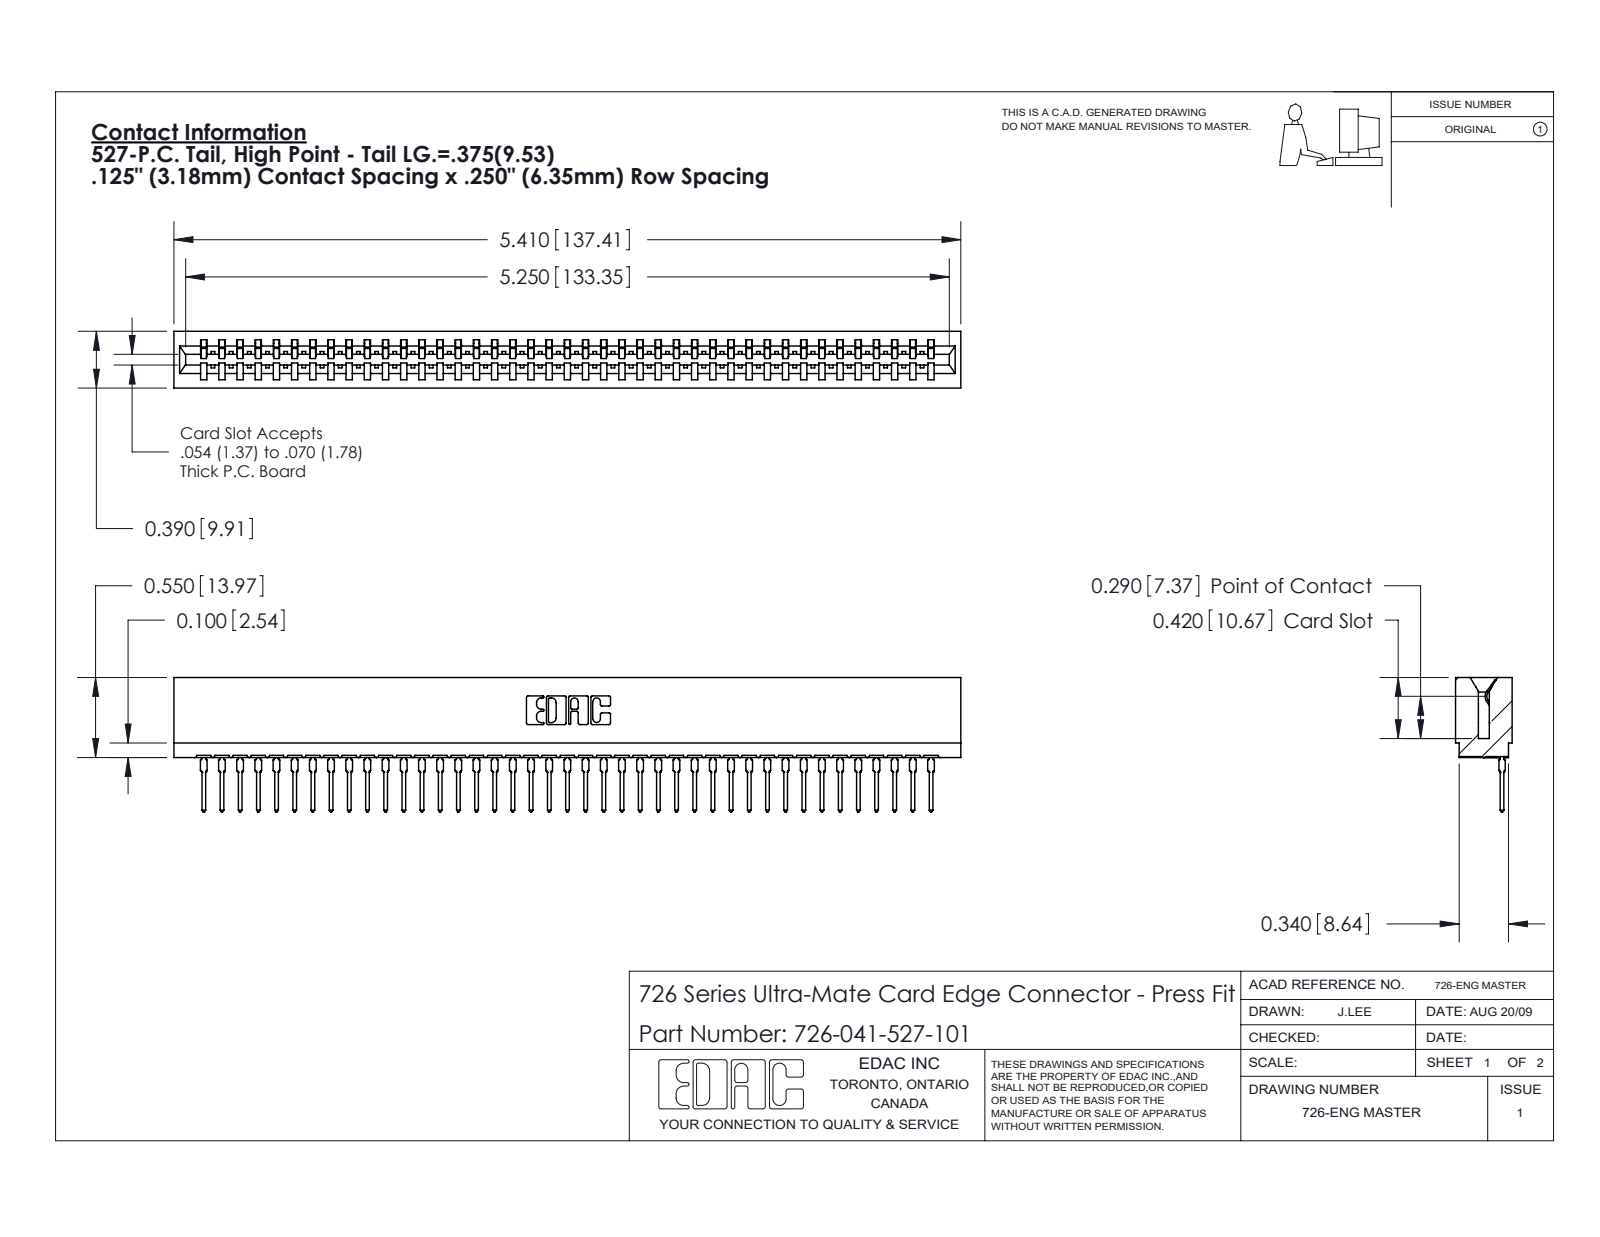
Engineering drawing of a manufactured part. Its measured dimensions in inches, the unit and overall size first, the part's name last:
Units: inches
Overall size (bounding box): 5.41 × 0.924 × 0.39
Partial cylindrical surfaces — rounded edges, fillets, slot ends (radius × count): R0.021 ×82, R0.015 ×42, R0.01 ×22, R0.007 ×6, R0.031 ×6, R0.005 ×4, R0.011 ×4, R0.026 ×3
Main face-to-face distances: 0.057, 0.333, 0.39, 0.025, 0.307, 0.25, 0.275, 0.083, 0.365, 0.032
Volume: 0.751 in³ · Surface area: 29.47 in²
Bodies: 42 solids, 4525 faces (2638 planar, 821 cylindrical, 1066 other)
Part name (STEP PRODUCT): 746-292-001_527; 726 Part_.515 Slot Depth - 01; 726-041-527-101
STEP written by: SolidWorks 2020 (CONFIG_CONTROL_DESIGN)
